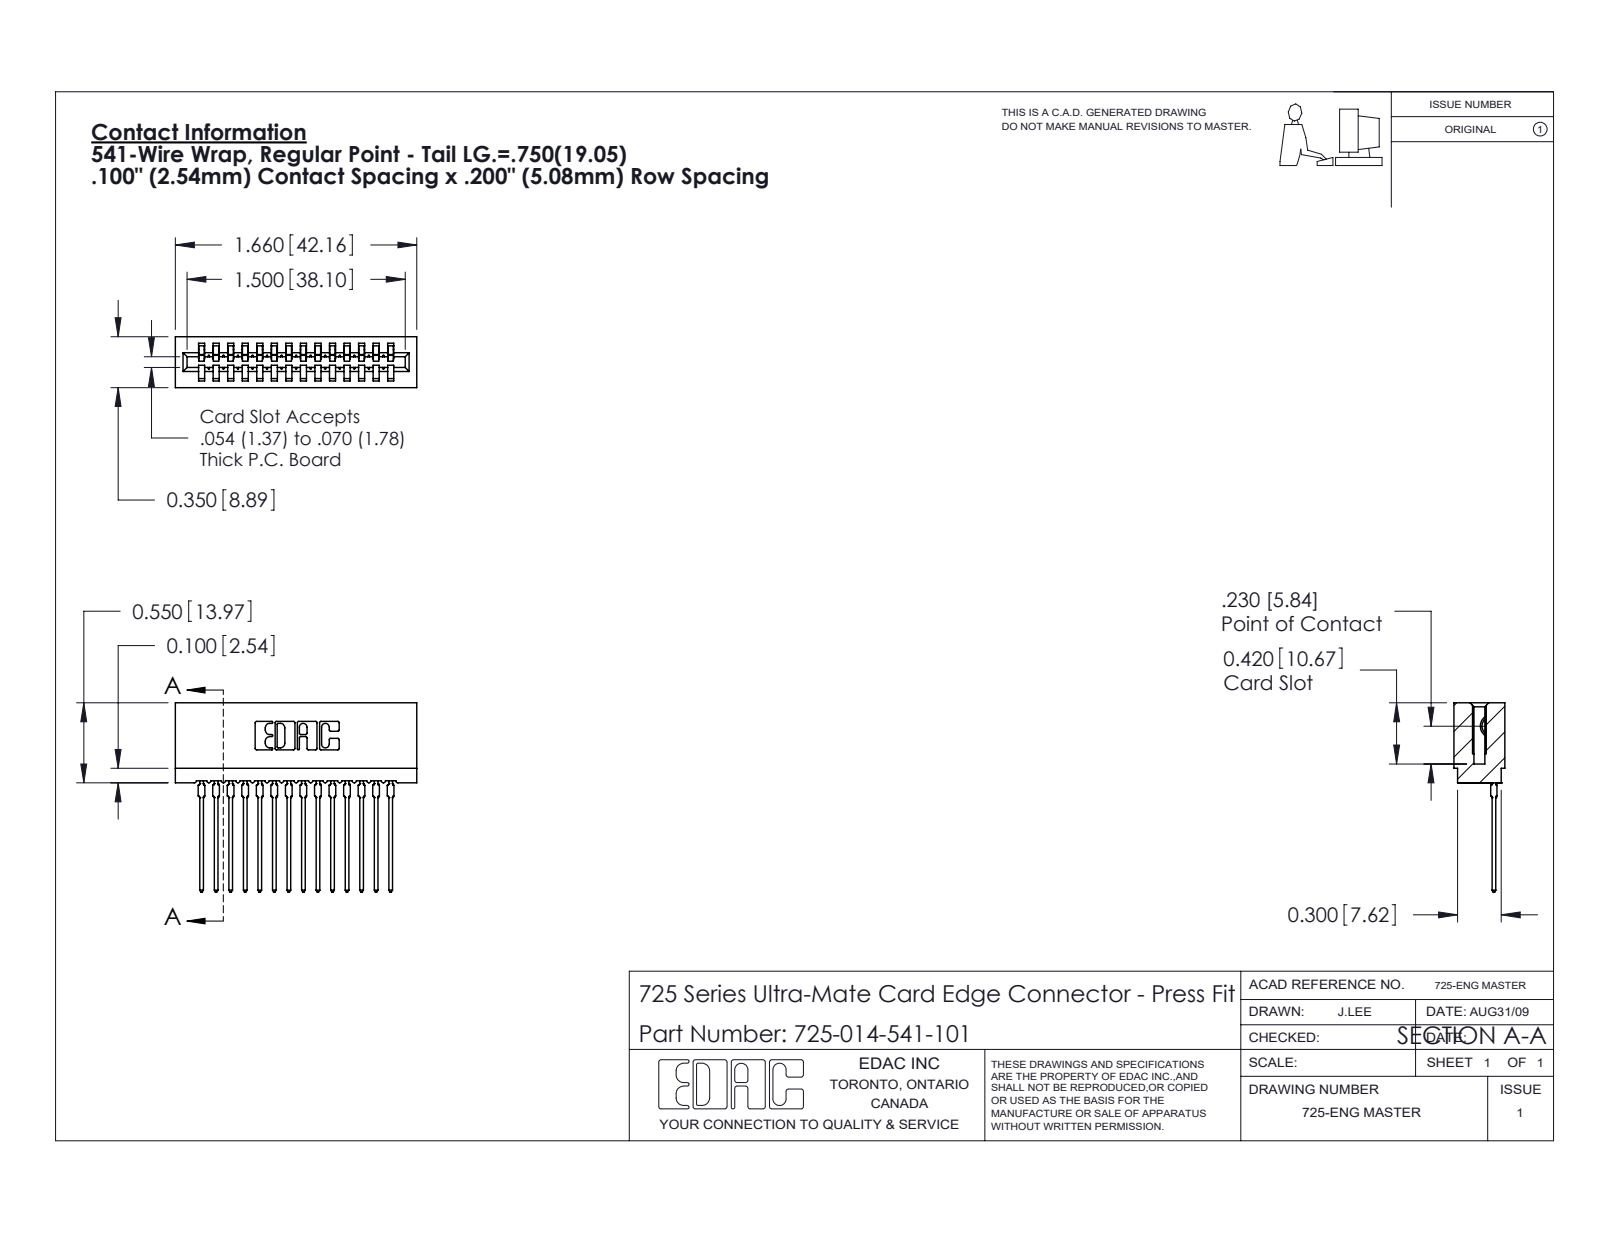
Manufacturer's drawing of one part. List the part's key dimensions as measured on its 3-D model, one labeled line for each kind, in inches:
Part name (STEP PRODUCT): 745-292-001_541; 725 Part_Insulator Option - 01; 725-014-541-101
STEP written by: SolidWorks 2020 (CONFIG_CONTROL_DESIGN)
Units: inches
Bodies: 15 solids, 1663 faces (993 planar, 306 cylindrical, 364 other)
Overall size (bounding box): 1.66 × 1.301 × 0.35
Volume: 0.208 in³ · Surface area: 9.827 in²
Partial cylindrical surfaces — rounded edges, fillets, slot ends (radius × count): R0.015 ×28, R0.021 ×28, R0.01 ×22, R0.007 ×6, R0.031 ×6, R0.005 ×4, R0.011 ×4, R0.026 ×3
Main face-to-face distances: 0.1, 0.2, 0.3, 0.4, 0.5, 0.35, 0.6, 0.063, 0.287, 0.212
